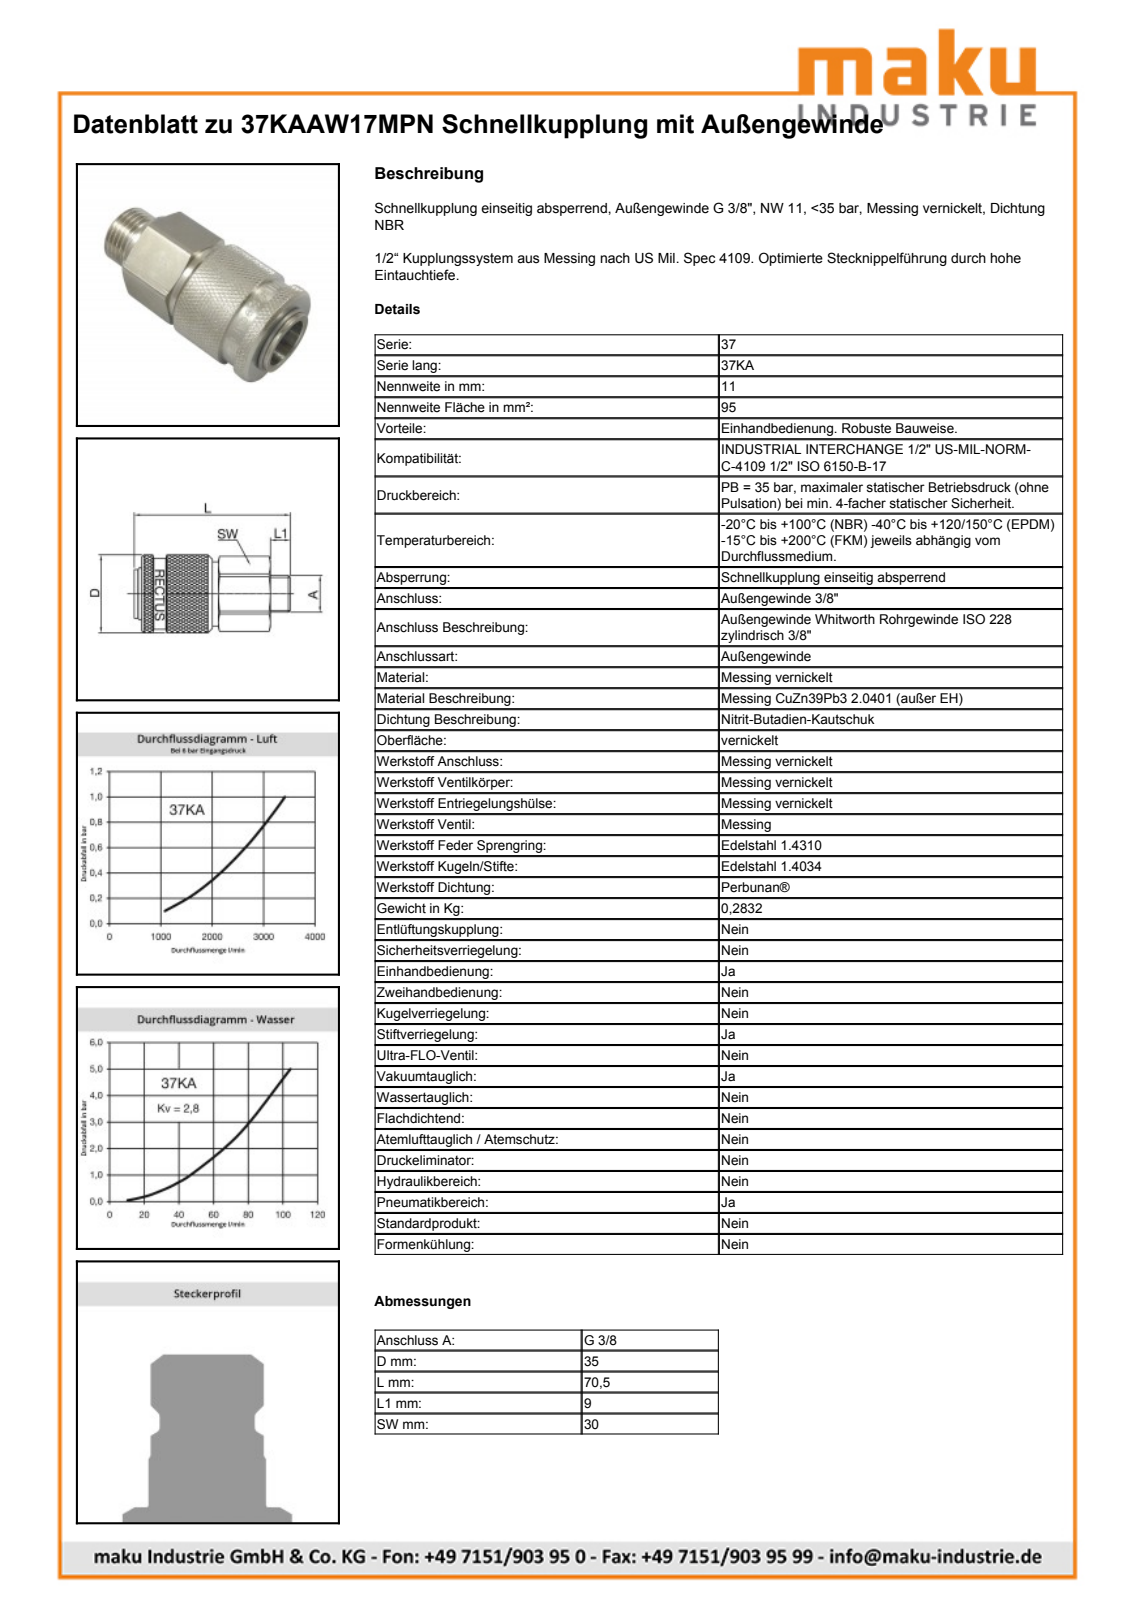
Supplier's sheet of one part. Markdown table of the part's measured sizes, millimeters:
| quantity | value |
| --- | --- |
| part name | D111127 |
| STEP written by | Autodesk Inventor 2013 (AUTOMOTIVE_DESIGN) |
| units | millimeters |
| bodies | 1 solid, 475 faces (165 planar, 54 cylindrical, 256 other) |
| overall size | 70.5 × 35.2 × 35.2 |
| volume | 50 176 mm³ |
| surface area | 13 161 mm² |
| round holes (diameter × count) | 29.2 × 1, 29.9 × 1 |
| round bosses / shafts (diameter × count) | 35.2 × 1, 32 × 1, 29 × 1, 26.39 × 1, 22 × 1, 20.6 × 1, 16.66 × 1 |
| partial cylindrical surfaces (radius × count) | 15.9 × 1, 16.93 × 1 |
| main face-to-face distances | 30, 58.3, 3.2, 61.5, 70.5, 67.3, 9, 32, 33, 29.8 |
